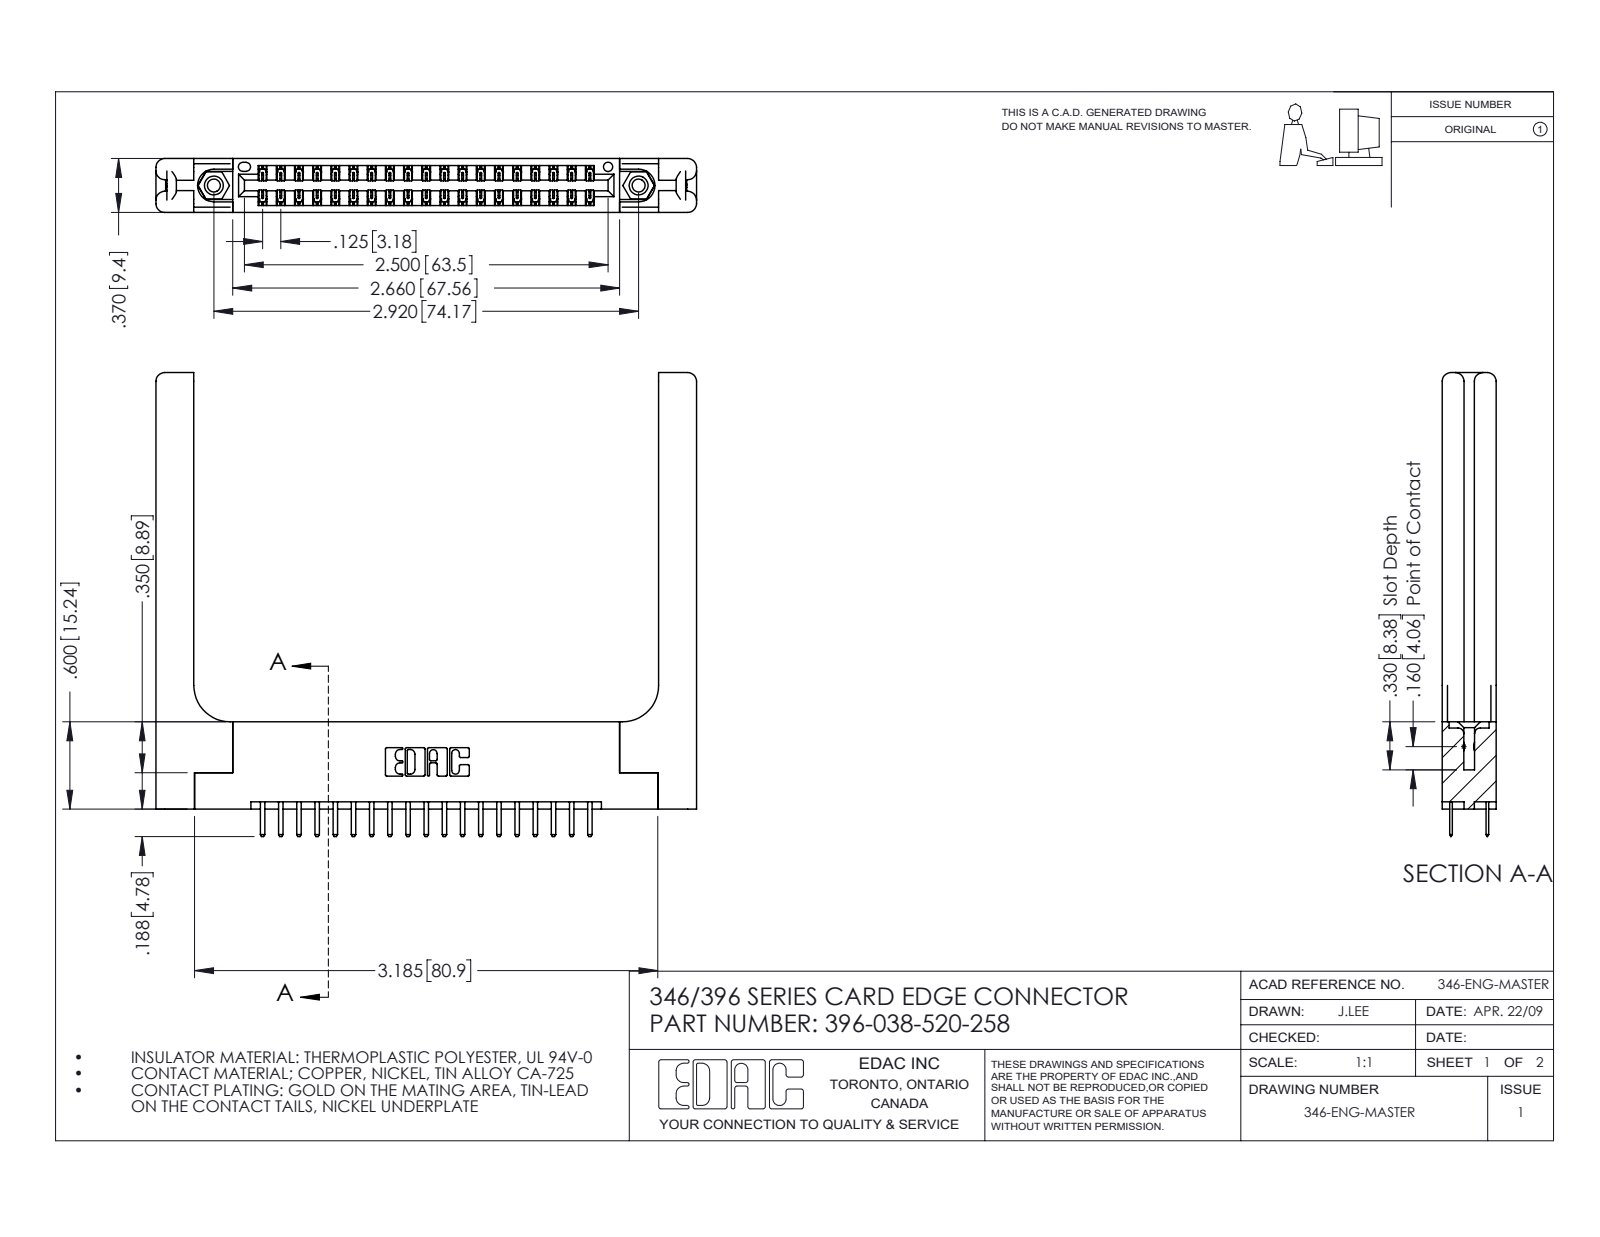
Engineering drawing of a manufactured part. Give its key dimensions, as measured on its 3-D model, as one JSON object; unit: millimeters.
{"part_name": "346 Part_Flush Mounting Lugs - 0.156 Dia-TH; 345-250-001_345-250-001-102; 345-292-001_345-293-120; 396-038-520-258 (+1 more)", "step_written_by": "SolidWorks 2016 (CONFIG_CONTROL_DESIGN)", "units": "millimeters", "bodies": {"solids": 43, "faces": 2506, "planar": 1630, "cylindrical": 816, "other": 60}, "overall_size": [94.4, 81, 9.4], "volume_mm3": 16500, "surface_area_mm2": 16950, "round_holes": [[2.3, 2], [3.2, 2], [4, 2], [1.6, 1]], "round_bosses_or_shafts": [[3.9, 2]], "partial_cylinders_radius": [[0.2, 57], [0.3, 42], [0.3, 22], [1.5, 16], [0.2, 6], [0.8, 6], [0.7, 3], [0.4, 2]], "face_to_face_distances": [9.4, 3.8, 1.8, 3.8, 1.2, 8.2, 6.4, 2.6, 5.6, 4.4], "hole_center_spacings": [6.2, 68.9, 74.2]}
